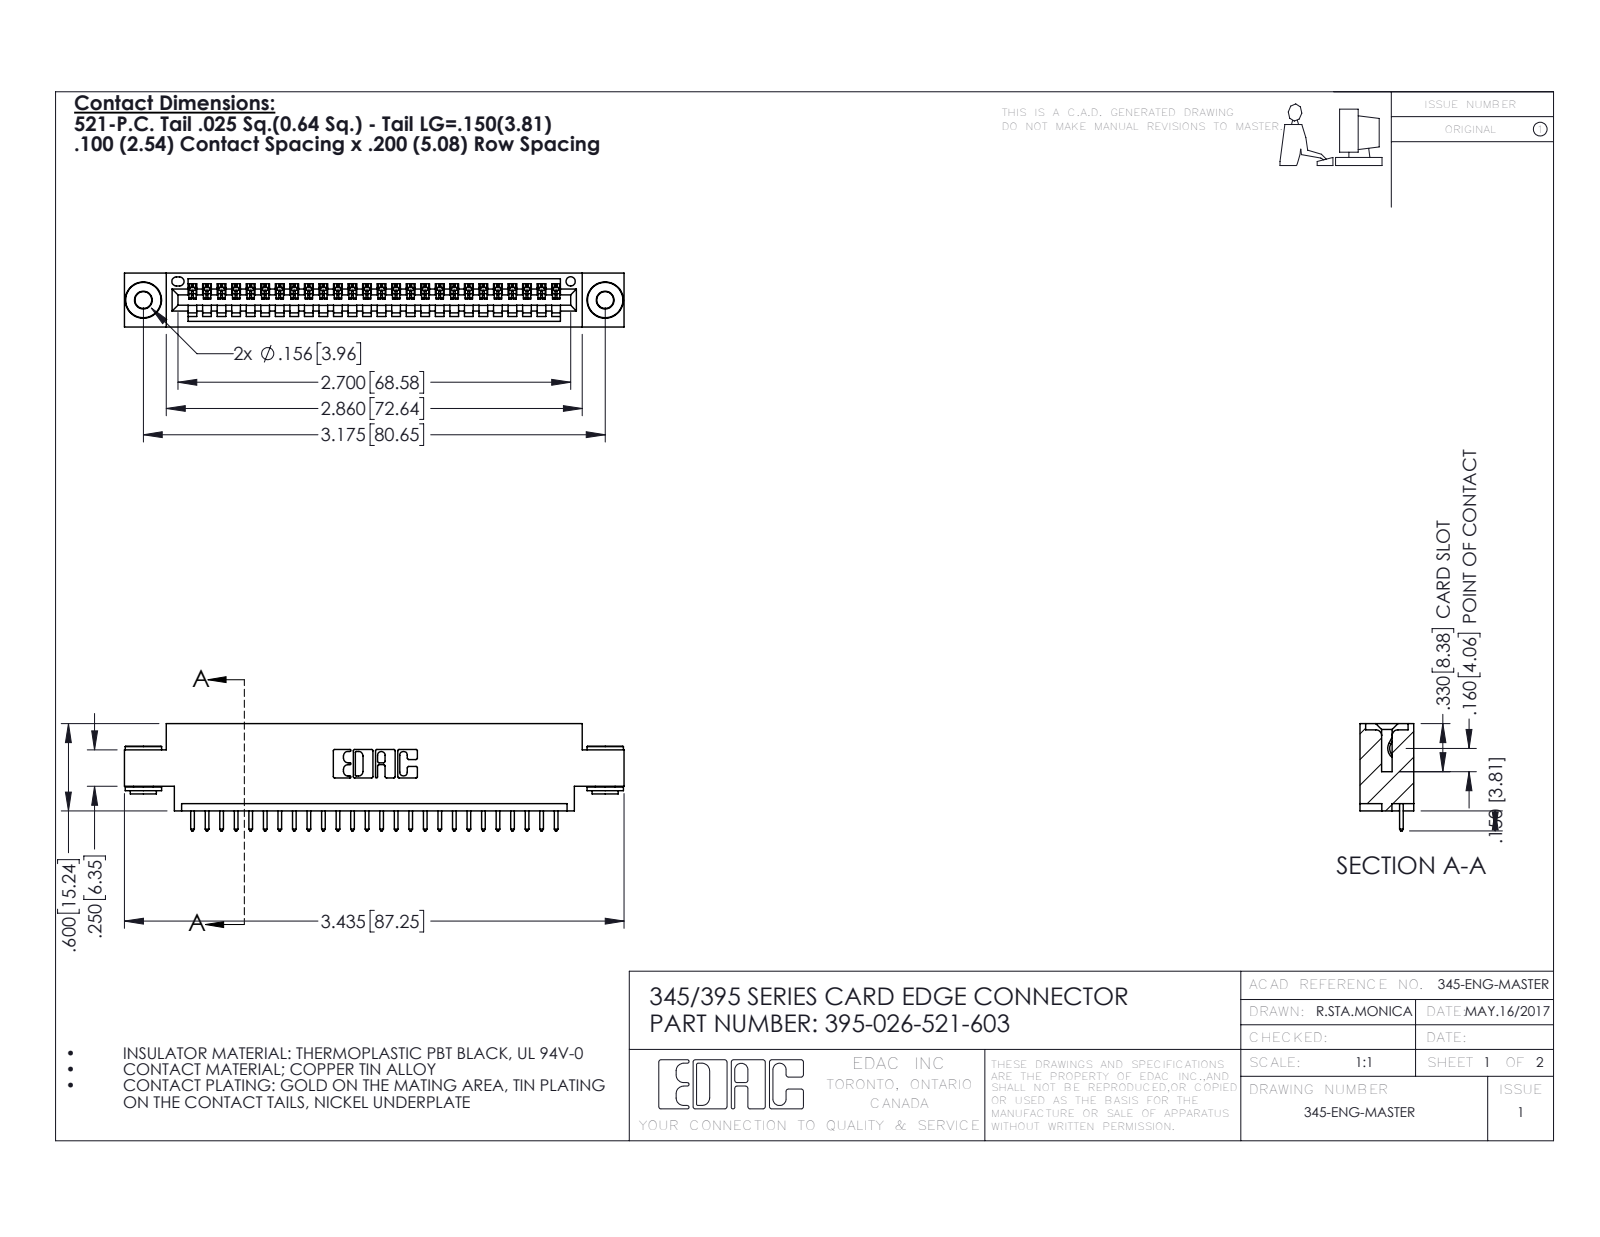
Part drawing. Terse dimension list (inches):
name: 395-026-521-603; 345-250-002_345-250-002-102; 345-292-001_345-293-121; 345 Part_0.170 Offset - 0.156 Dia-TH
written by: SolidWorks 2016 (CONFIG_CONTROL_DESIGN)
unit: in
bodies: 29 solids, 1676 faces (1134 planar, 534 cylindrical, 8 other)
size: 3.435 × 0.737 × 0.37
volume: 0.487 in³; area: 16.2 in²
holes: 2× ⌀0.116, 2× ⌀0.156, 1× ⌀0.064
bosses: 2× ⌀0.25, 2× ⌀0.18, 2× ⌀0.136
rounds: 52× R0.006, 52× R0.01, 22× R0.01, 6× R0.007, 6× R0.031, 3× R0.026, 2× R0.031, 2× R0.04
face distances: 0.072, 0.298, 0.37, 0.2, 0.098, 0.272, 0.025, 0.225, 0.175, 0.149
hole spacings: 0.27, 2.94, 3.175
